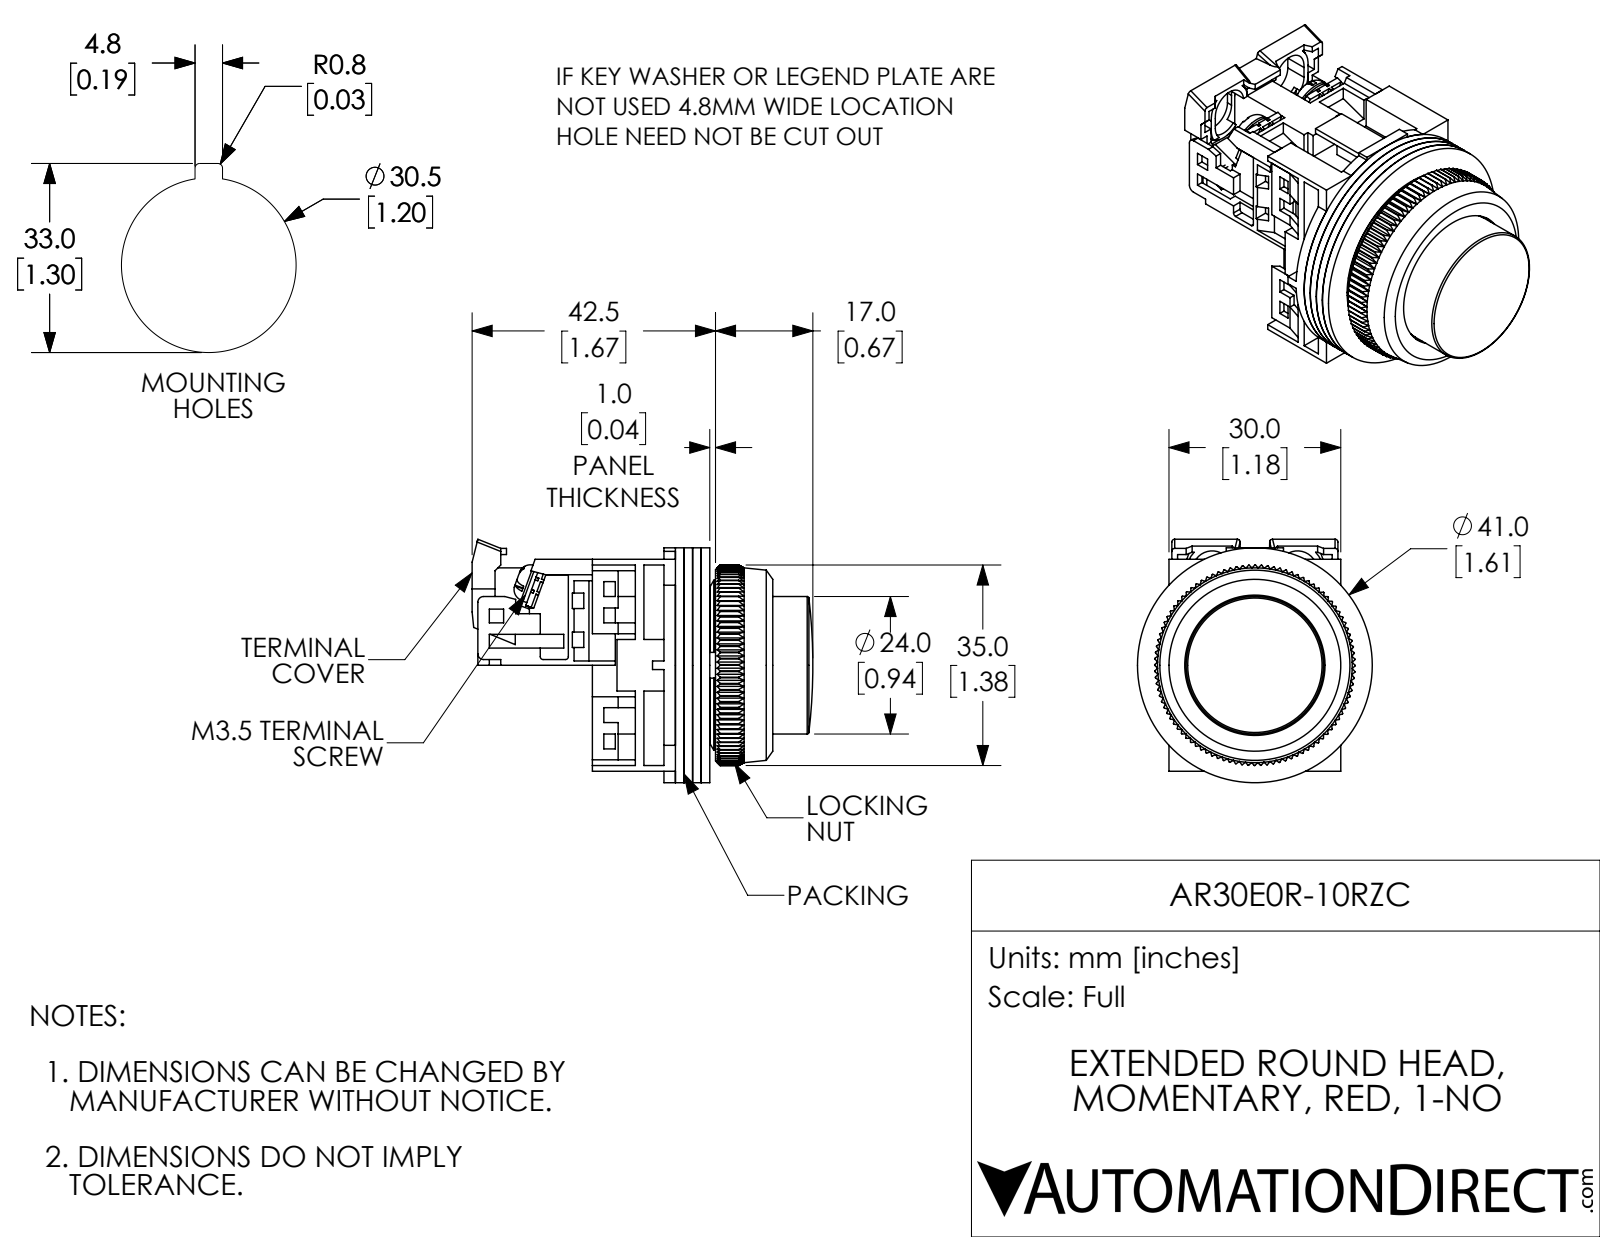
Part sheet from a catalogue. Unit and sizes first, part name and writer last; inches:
Units: inches
Overall size (bounding box): 2.342 × 1.673 × 1.614
Round holes (diameter × count): ⌀0.138 ×4, ⌀0.142 ×2, ⌀0.118 ×1, ⌀0.472 ×1, ⌀0.709 ×1, ⌀0.787 ×1, ⌀0.945 ×1, ⌀0.965 ×1, ⌀1.122 ×1, ⌀1.252 ×1
Round bosses / shafts (diameter × count): ⌀0.26 ×2, ⌀0.138 ×2, ⌀1.614 ×1, ⌀1.181 ×1, ⌀0.866 ×1, ⌀0.551 ×1
Partial cylindrical surfaces — rounded edges, fillets, slot ends (radius × count): R0.059 ×8, R0.02 ×6, R0.039 ×2, R0.138 ×2, R0.177 ×2, R0.118 ×1, R0.398 ×1, R0.449 ×1
Main face-to-face distances: 0.059, 0.118, 0.177, 0.039, 0.197, 0.079, 0.276, 0.689, 0.728, 0.602
Hole centre spacings: 0.579, 0.61
Volume: 1.642 in³ · Surface area: 48.85 in²
Bodies: 16 solids, 1234 faces (775 planar, 249 cylindrical, 210 other)
Part name (STEP PRODUCT): AR30E0R-10RZC
STEP written by: SolidWorks 2017 (AUTOMOTIVE_DESIGN)
